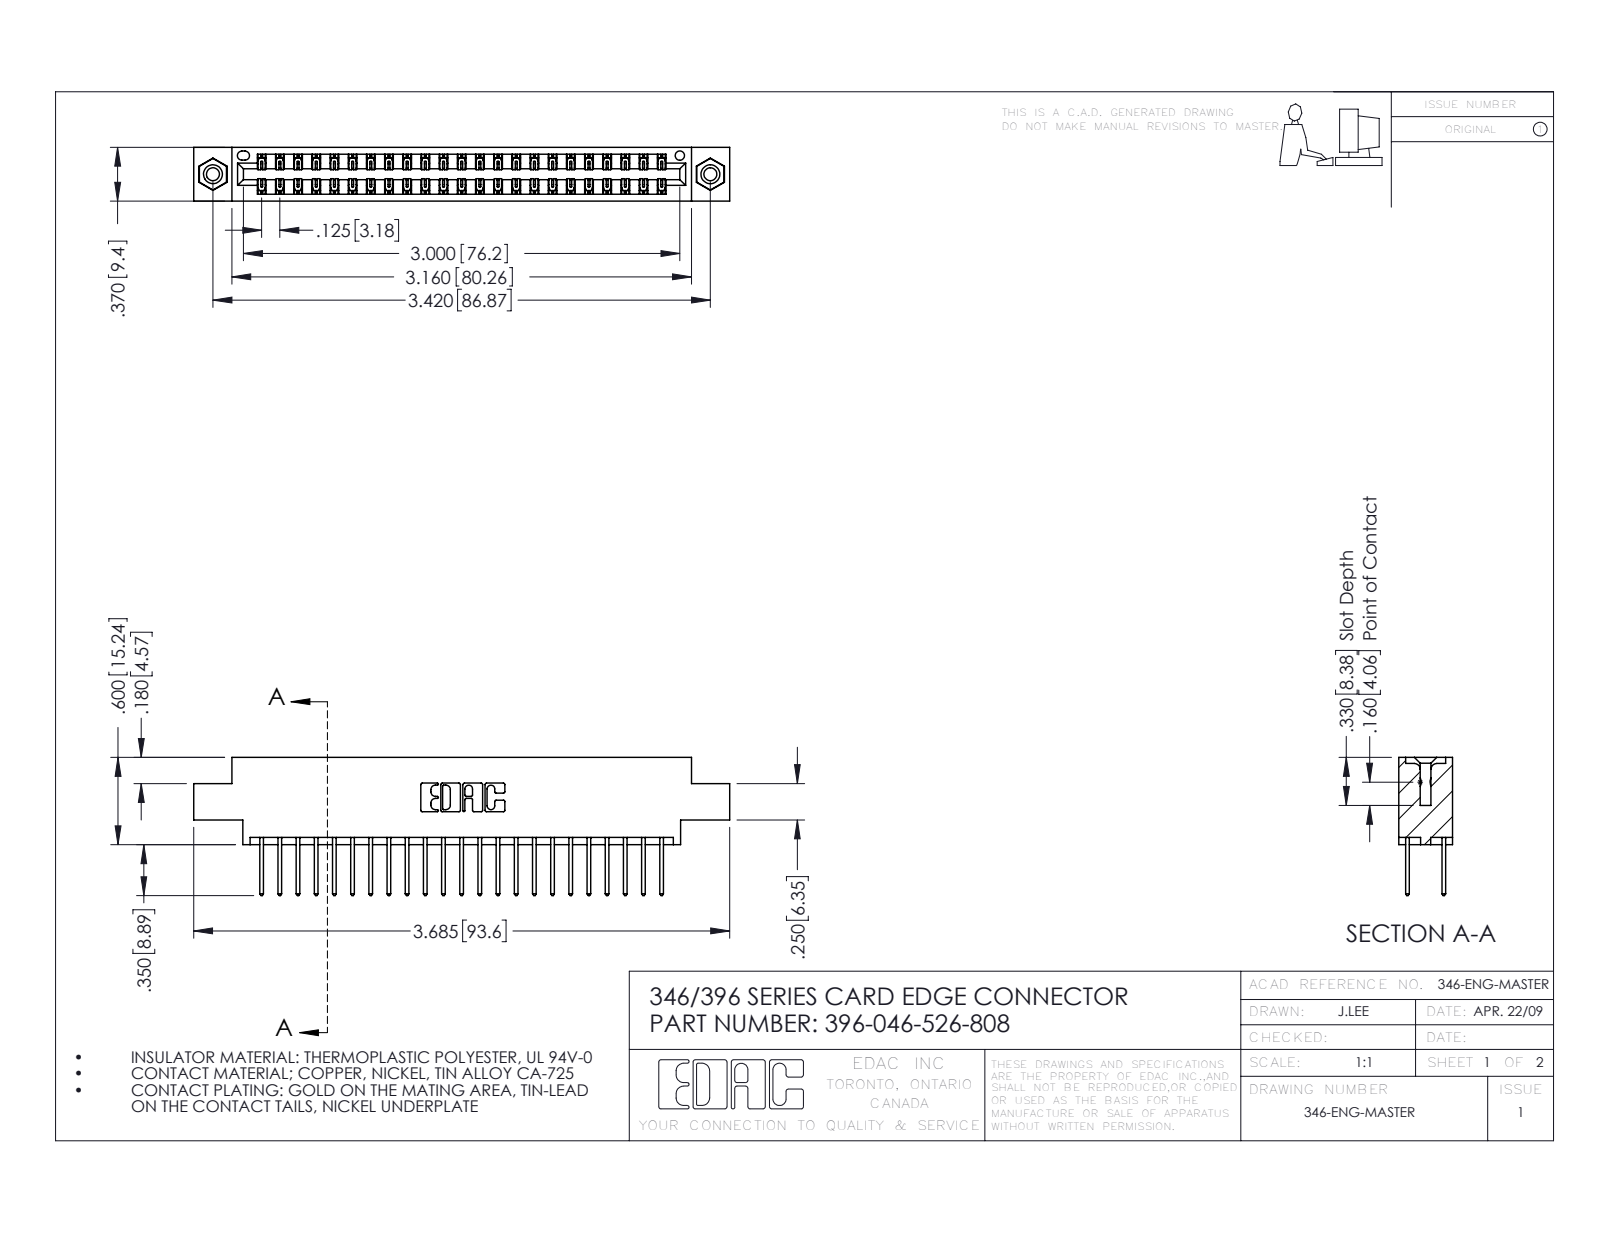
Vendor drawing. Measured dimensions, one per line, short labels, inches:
name: 345-250-001_345-250-003-102; 396-046-526-808; 346 Part_0.170 Offset - 0.156 Dia-TI; 345-292-001_345-293-126
written by: SolidWorks 2016 (CONFIG_CONTROL_DESIGN)
unit: in
bodies: 49 solids, 2578 faces (1722 planar, 840 cylindrical, 16 other)
size: 3.685 × 0.95 × 0.37
volume: 0.543 in³; area: 19.32 in²
holes: 2× ⌀0.089, 2× ⌀0.125, 2× ⌀0.156, 1× ⌀0.064
bosses: 2× ⌀0.155
rounds: 69× R0.006, 46× R0.01, 22× R0.01, 6× R0.007, 6× R0.031, 3× R0.026, 2× R0.014, 2× R0.022
face distances: 0.048, 0.322, 0.25, 0.37, 0.072, 0.298, 0.025, 0.275, 0.222, 0.148
hole spacings: 0.246, 3.212, 3.42
